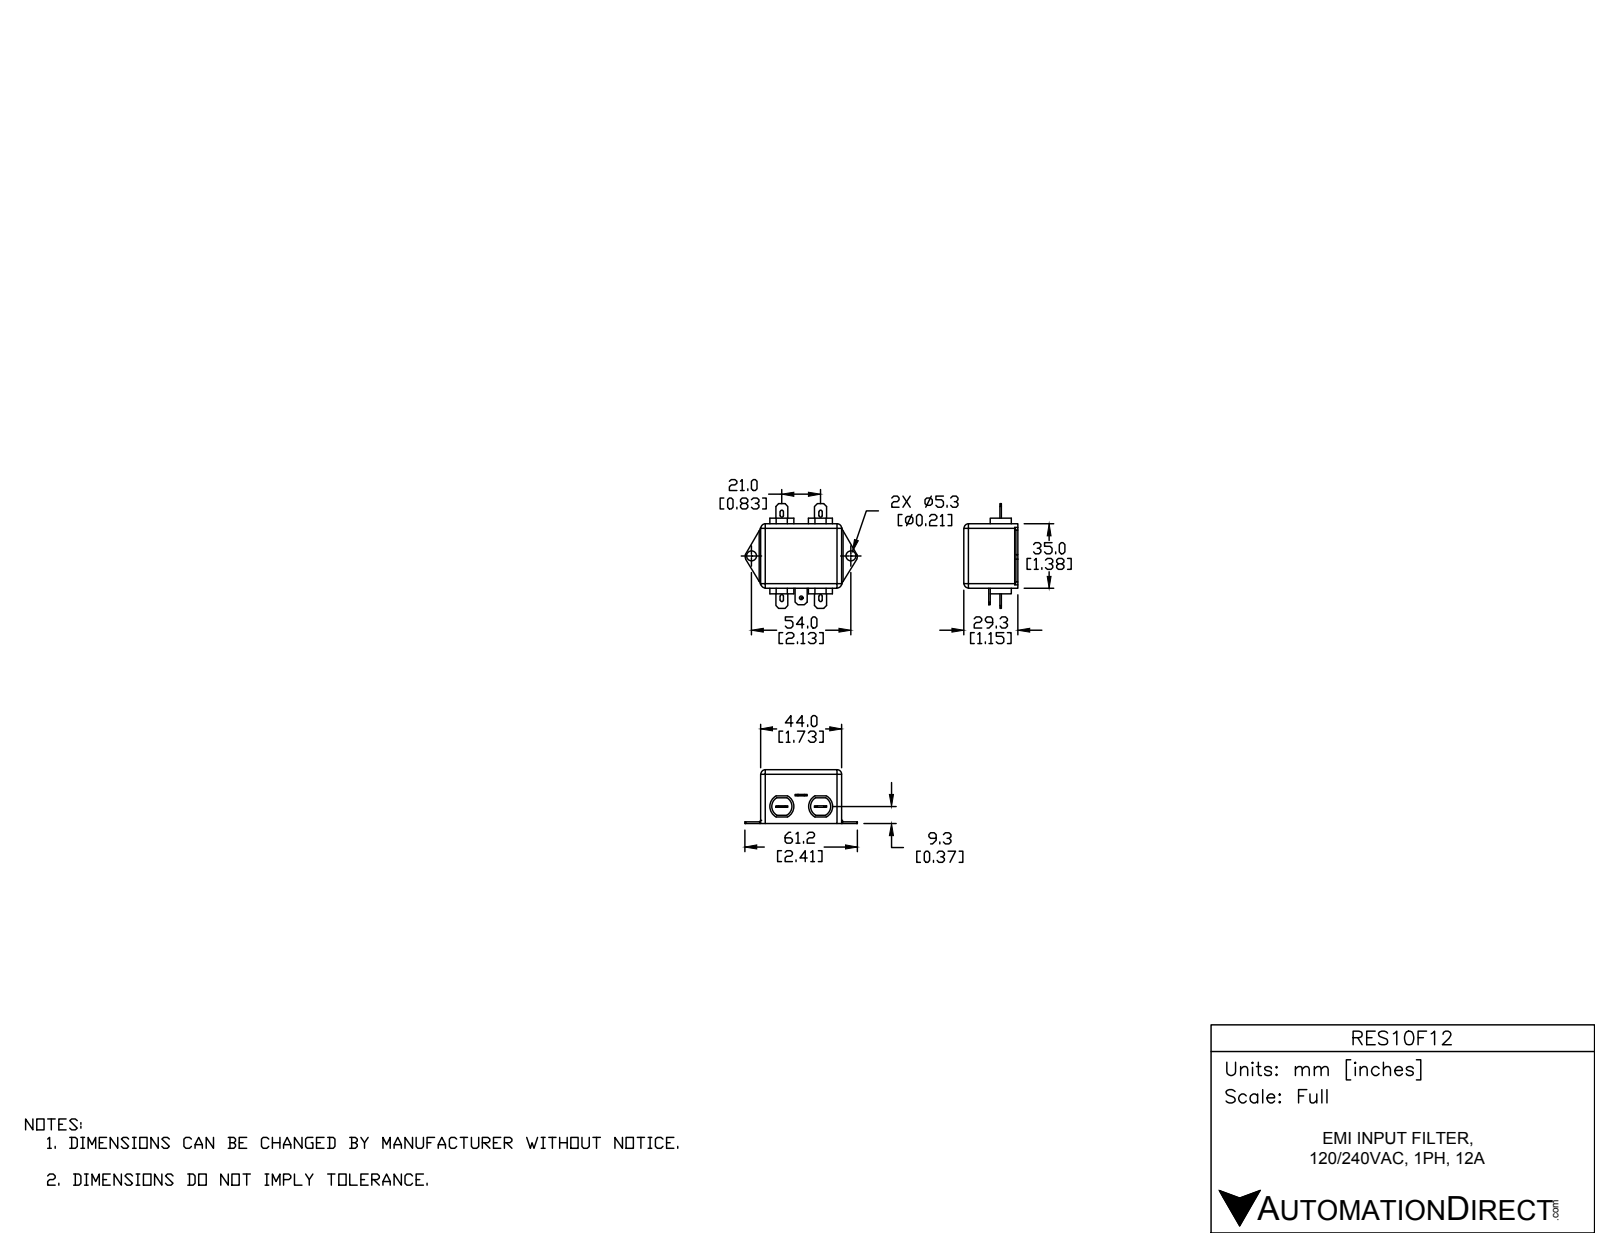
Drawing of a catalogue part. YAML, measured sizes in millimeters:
part_name: "RES10F12"
step_written_by: "SolidWorks 2015 (AUTOMOTIVE_DESIGN)"
units: millimeters
bodies: {solids: 1, faces: 137, planar: 79, cylindrical: 54, other: 4}
overall_size: [62.99, 56.8, 29.3]
volume: 46184
surface_area: 9278
round_holes:
  - {diameter: 5.3, count: 2}
  - {diameter: 2, count: 1}
partial_cylinders:
  - {radius: 2.5, count: 10}
  - {radius: 0.9, count: 8}
  - {radius: 0.75, count: 2}
  - {radius: 5.5, count: 2}
  - {radius: 6.5, count: 2}
face_to_face_distances: [29.3, 35, 44, 1.4, 36.4, 1, 0.8, 7.9, 8.9, 20.4]
hole_center_spacings: [35.34, 54]
